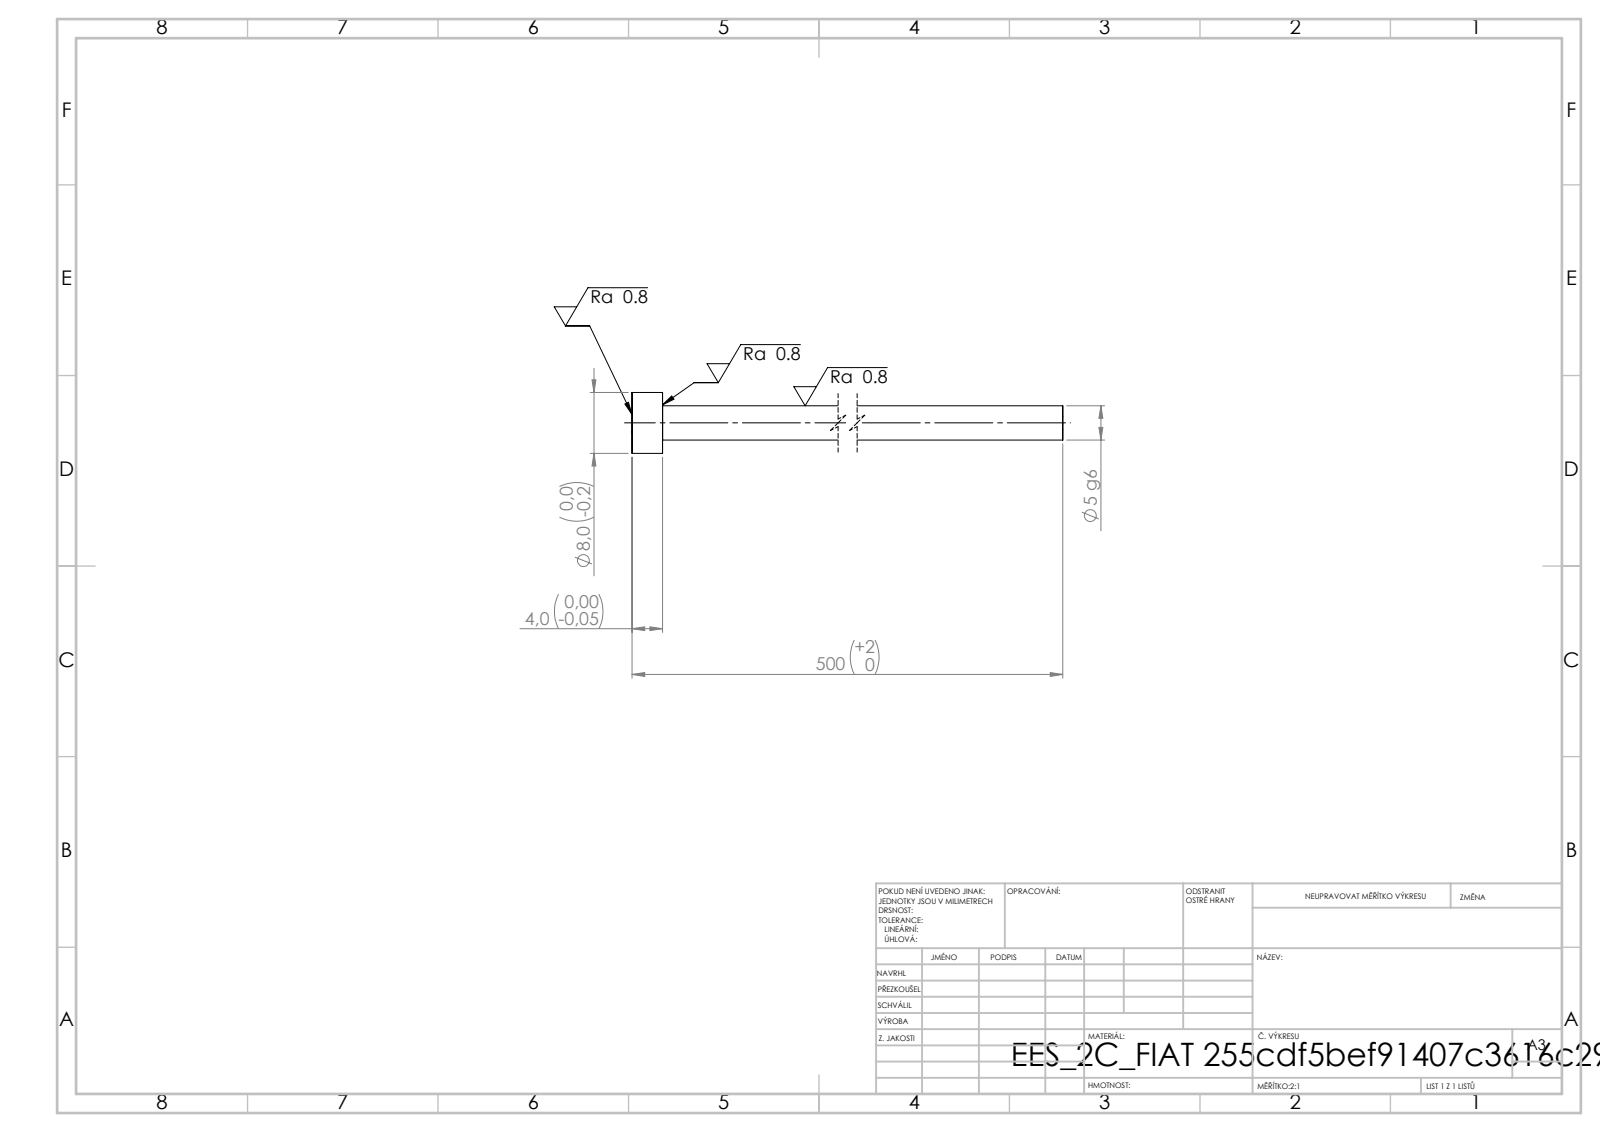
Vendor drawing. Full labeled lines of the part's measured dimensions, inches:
STEP written by: SolidWorks 2019 (CONFIG_CONTROL_DESIGN)
Units: inches
Bodies: 1 solid, 7 faces (3 planar, 4 cylindrical, 0 other)
Overall size (bounding box): 19.685 × 0.315 × 0.315
Volume: 0.494 in³ · Surface area: 11.18 in²
Round bosses / shafts (diameter × count): ⌀0.315 ×1, ⌀0.177 ×1
Main face-to-face distances: 0.157, 19.685, 19.528
